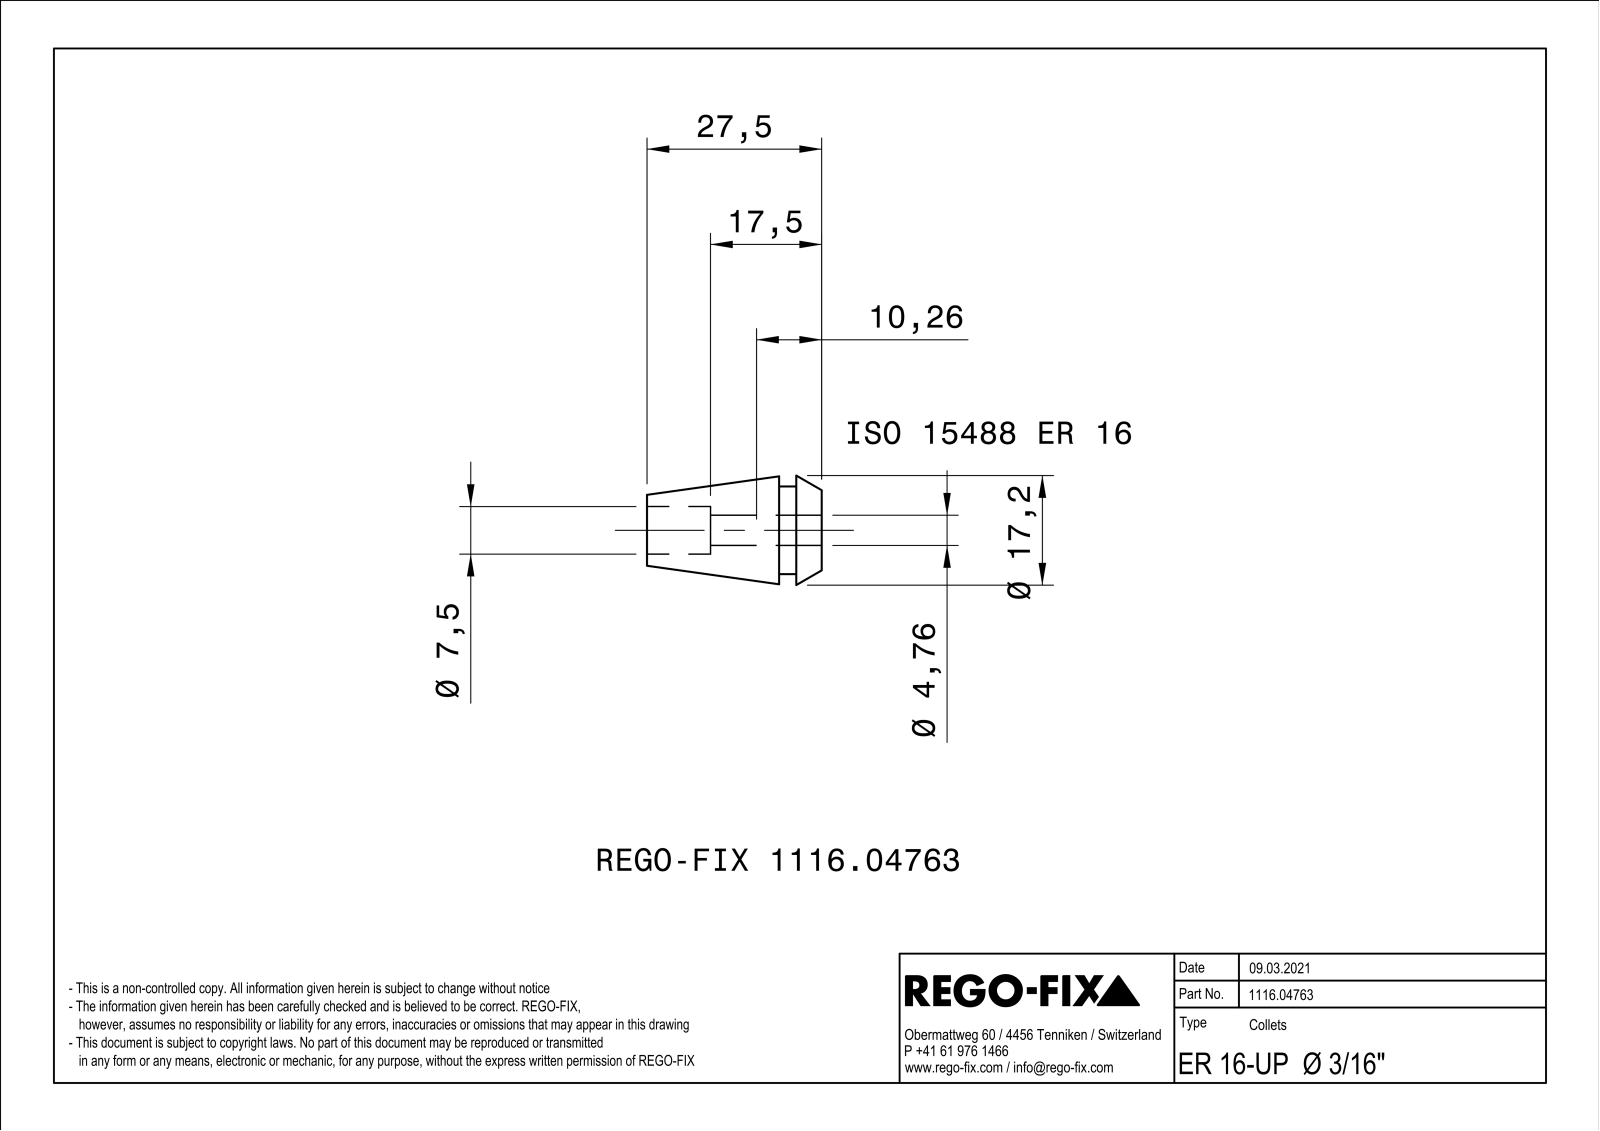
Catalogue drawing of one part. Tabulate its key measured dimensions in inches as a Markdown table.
| quantity | value |
| --- | --- |
| part name | NOCUT |
| STEP written by | SIEMENS PLM Software Solid Edge ST10 (AUTOMOTIVE_DESIGN) |
| units | inches |
| bodies | 1 solid, 240 faces (112 planar, 32 cylindrical, 96 other) |
| overall size | 1.083 × 0.679 × 0.679 |
| volume | 0.164 in³ |
| surface area | 7.59 in² |
| round holes (diameter × count) | 0.295 × 1 |
| partial cylindrical surfaces (radius × count) | 0.094 × 1, 0.272 × 1 |
| main face-to-face distances | 0.024, 0.126, 0.15, 0.157, 0.264, 0.106, 0.276, 1.083, 0.925, 0.819 |
